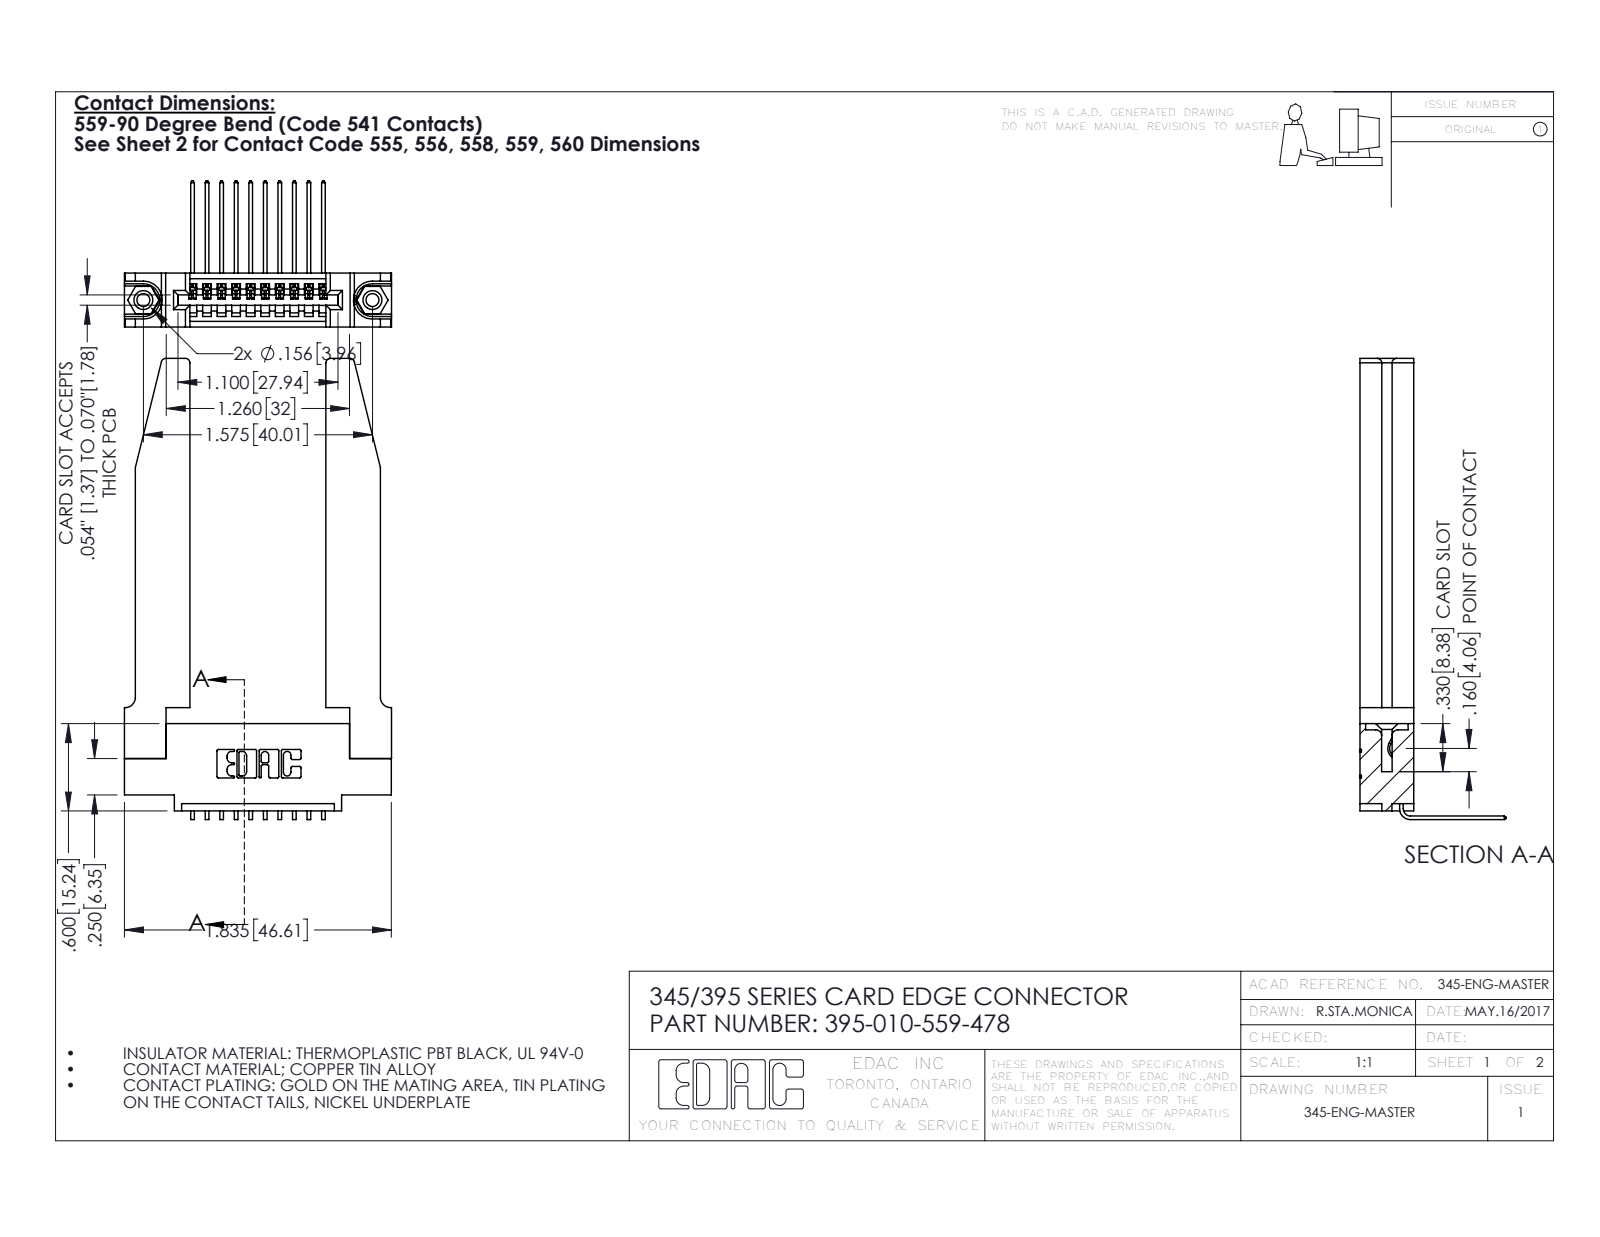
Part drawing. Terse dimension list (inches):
name: 345 Part_0.110 Offset - 0.156 Dia-TH; 395-010-559-478; 345-292-001_558 559 Tail - 1; 345-220-078_345-220-078 (+1 more)
written by: SolidWorks 2016 (CONFIG_CONTROL_DESIGN)
unit: in
bodies: 15 solids, 964 faces (646 planar, 266 cylindrical, 52 other)
size: 3.169 × 1.836 × 1.005
volume: 0.726 in³; area: 18.87 in²
holes: 2× ⌀0.089, 2× ⌀0.125, 2× ⌀0.156, 1× ⌀0.064
bosses: 2× ⌀0.155
rounds: 22× R0.01, 20× R0.006, 8× R0.03, 6× R0.007, 6× R0.031, 3× R0.026, 2× R0.031, 2× R0.04
face distances: 0.37, 0.072, 0.15, 0.298, 0.148, 0.22, 0.077, 0.935, 0.2, 0.071
hole spacings: 0.27, 1.344, 1.575
